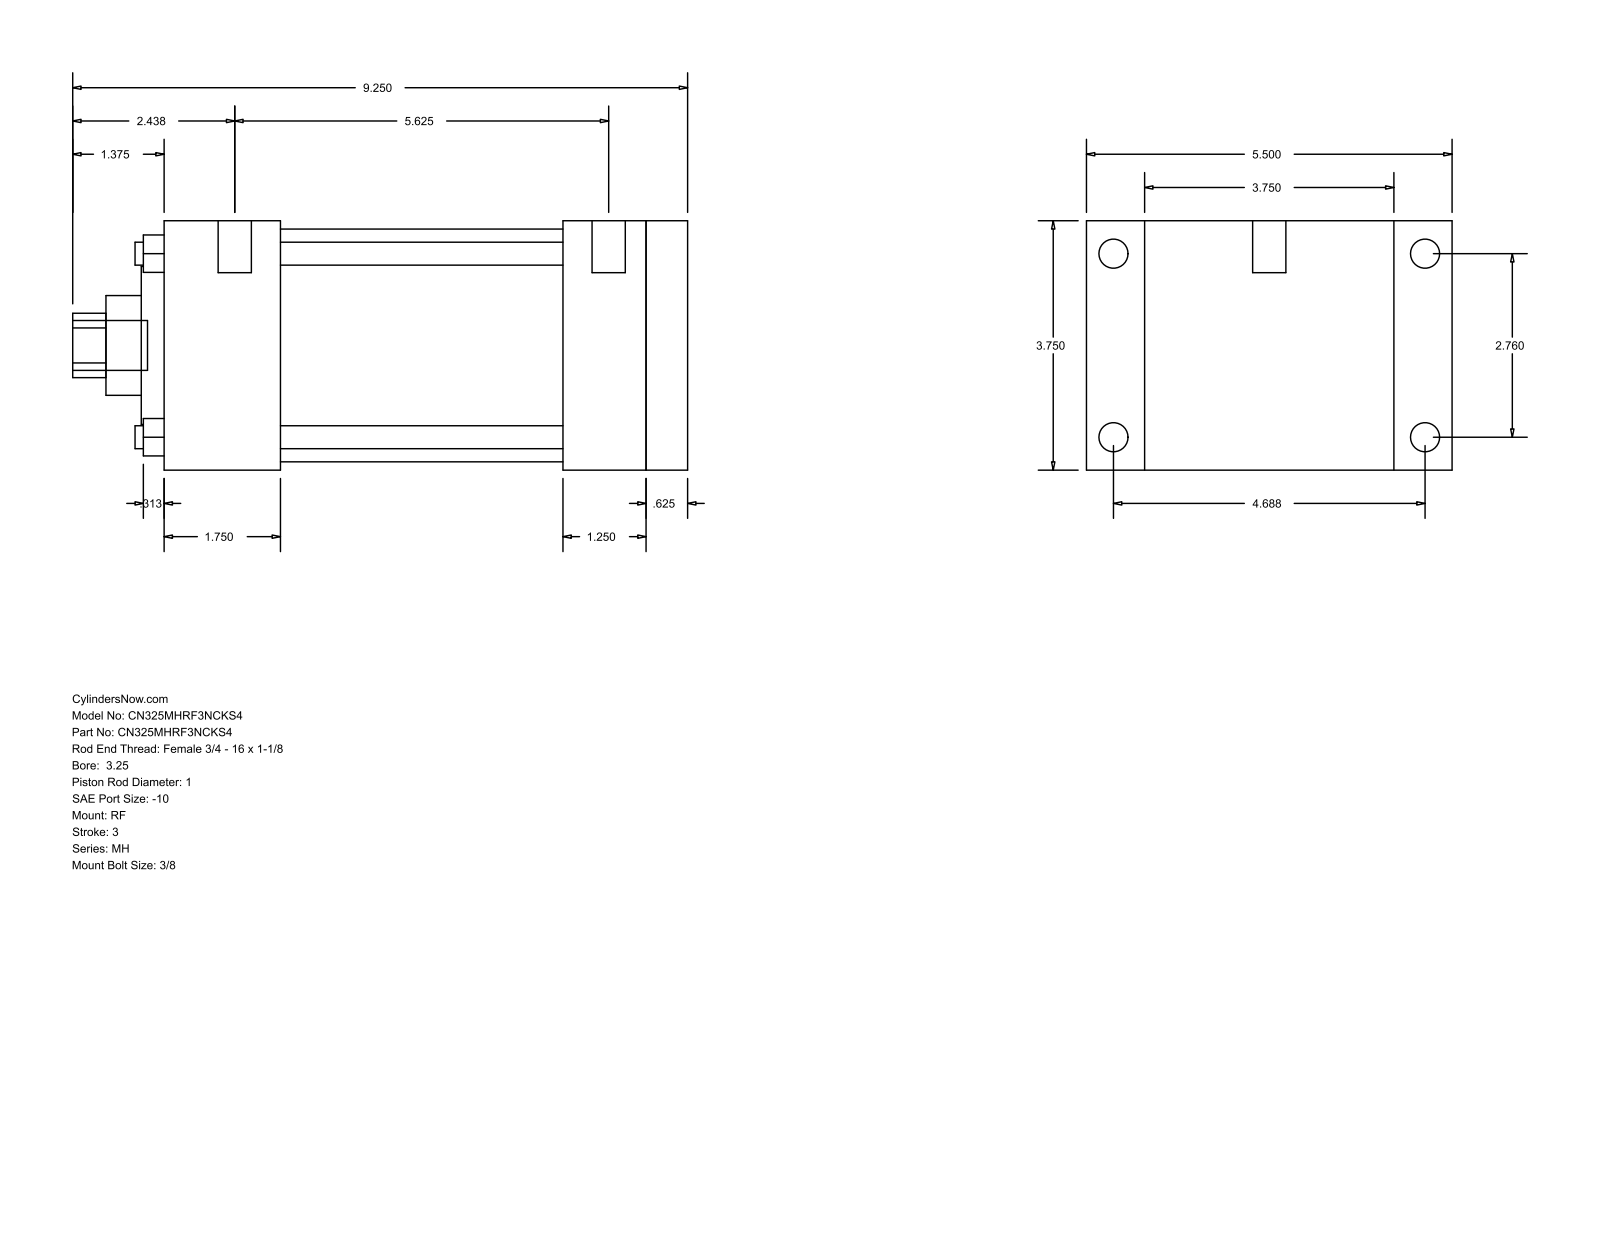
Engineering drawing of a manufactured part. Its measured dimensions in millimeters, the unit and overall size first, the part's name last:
Units: millimetres
Overall size (bounding box): 234.95 × 139.7 × 95.25
Round holes (diameter × count): ⌀8.76 ×4, ⌀25.4 ×1, ⌀38.1 ×1, ⌀60.33 ×1, ⌀88.9 ×1
Round bosses / shafts (diameter × count): ⌀11.13 ×4, ⌀5.56 ×4, ⌀12.7 ×2, ⌀19.05 ×1
Partial cylindrical surfaces — rounded edges, fillets, slot ends (radius × count): R12.29 ×1
Main face-to-face distances: 95.24, 200.03, 184.15, 15.88, 22.23, 117.47, 44.46, 139.69, 155.57, 152.4
Hole centre spacings: 49.57, 70.1, 99.14
Bodies: 0 solids, 94 faces (65 planar, 29 cylindrical, 0 other)
Part name (STEP PRODUCT): MH_RF__0325_1
STEP written by: GSSL Pune (CONFIG_CONTROL_DESIGN)
